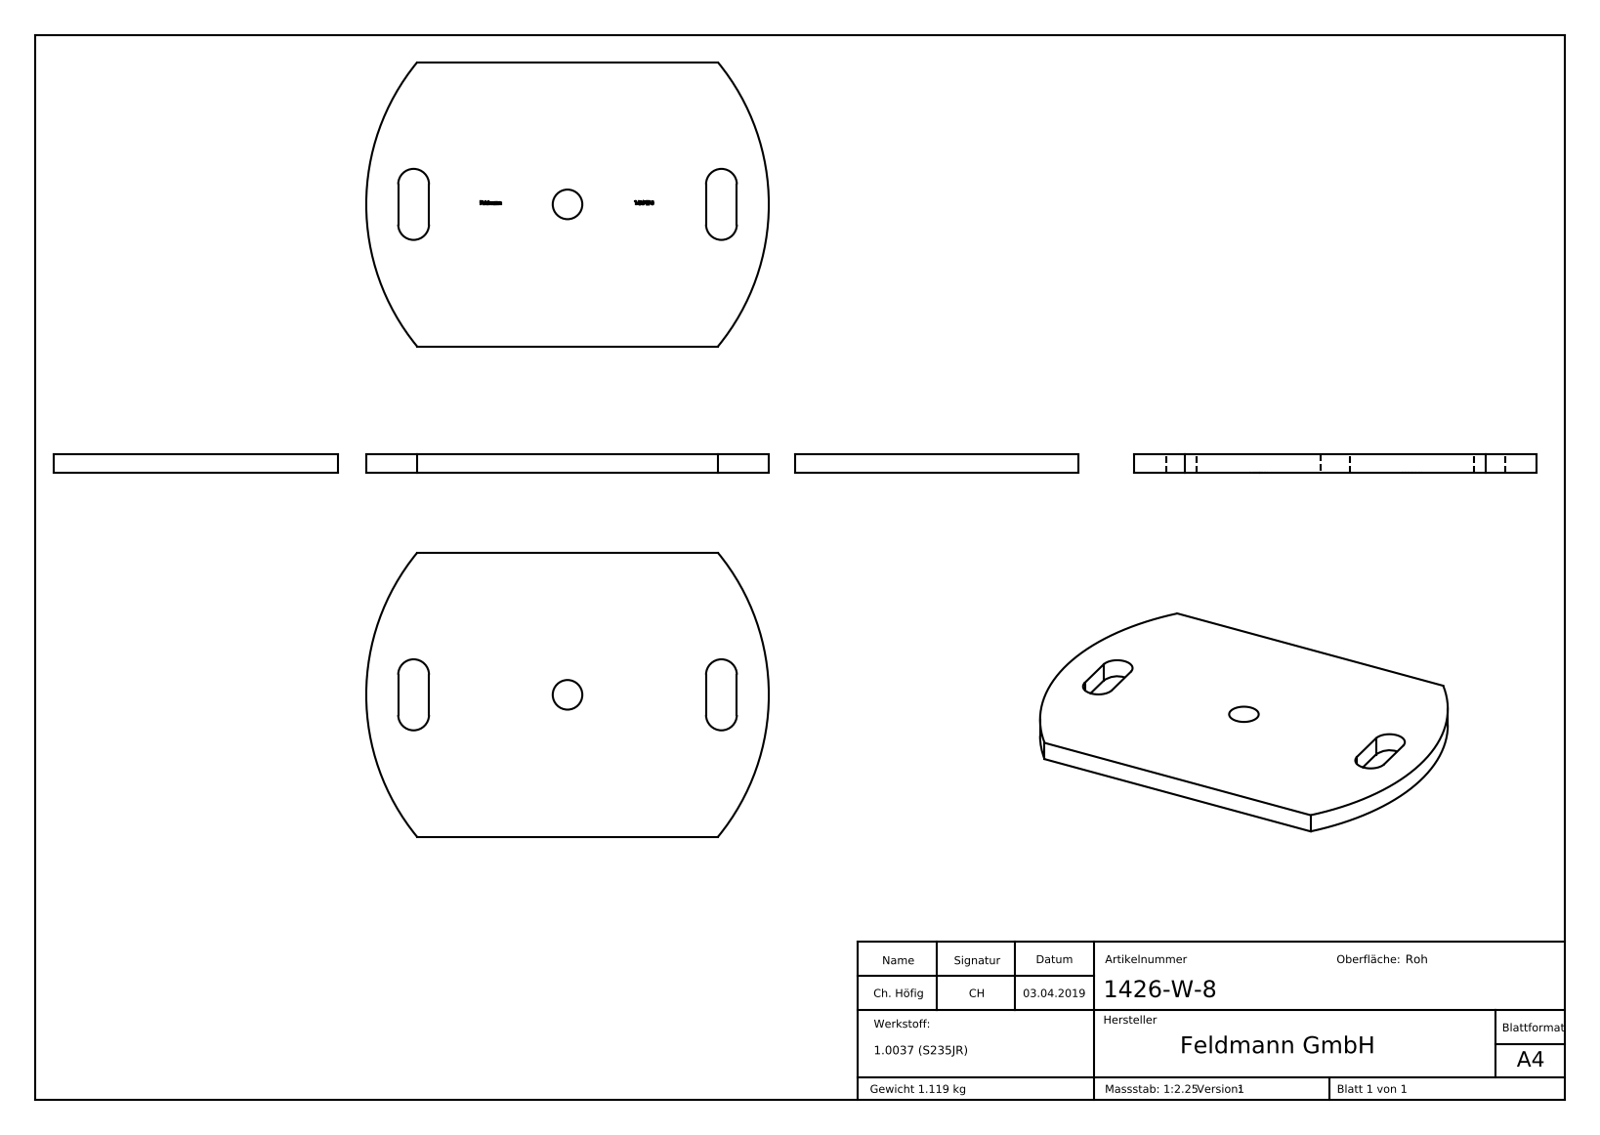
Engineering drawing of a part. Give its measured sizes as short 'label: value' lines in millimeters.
name: 1426-W-8
written by: SolidWorks 2015 (CONFIG_CONTROL_DESIGN)
unit: mm
bodies: 1 solid, 224 faces (134 planar, 10 cylindrical, 80 other)
size: 170 × 120 × 8
volume: 143 492 mm³; area: 41 506 mm²
holes: 1× ⌀12.5
rounds: 4× R6.5, 2× R94.47
face distances: 8, 120, 13, 130, 143, 117, 7.9, 60, 63.47, 2.02
